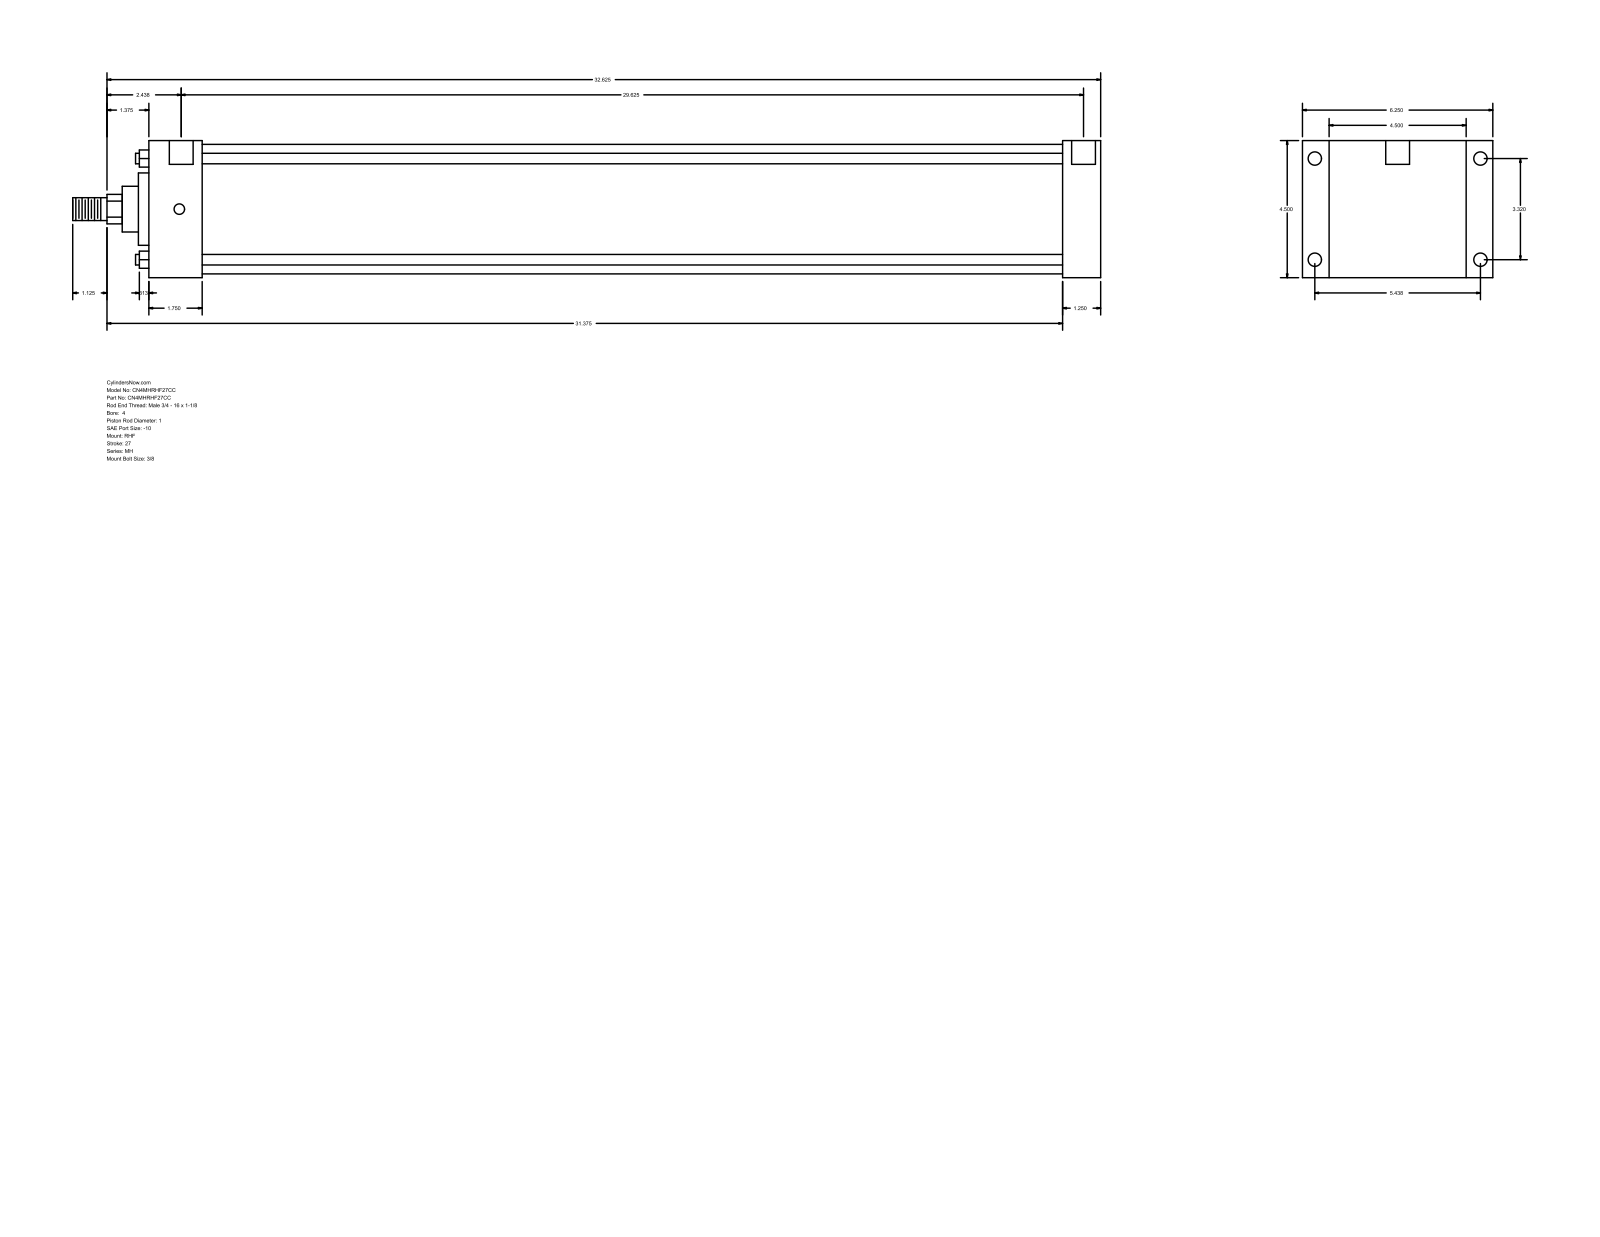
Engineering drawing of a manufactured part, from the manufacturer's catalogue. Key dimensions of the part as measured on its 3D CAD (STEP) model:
Part name (STEP PRODUCT): MH_RHF__0400_1
STEP written by: GSSL Pune (CONFIG_CONTROL_DESIGN)
Units: millimetres
Bodies: 0 solids, 90 faces (61 planar, 29 cylindrical, 0 other)
Overall size (bounding box): 857.25 × 158.75 × 114.3
Round holes (diameter × count): ⌀8.73 ×4, ⌀11.13 ×4, ⌀19.84 ×2
Round bosses / shafts (diameter × count): ⌀8.76 ×4, ⌀107.95 ×1, ⌀60.33 ×1, ⌀38.1 ×1, ⌀25.4 ×1, ⌀19.05 ×1
Partial cylindrical surfaces — rounded edges, fillets, slot ends (radius × count): R12.29 ×1
Main face-to-face distances: 114.3, 793.75, 762, 31.75, 22.23, 136.53, 44.46, 717.54, 749.29, 158.76
Hole centre spacings: 84.32, 138.12, 161.82, 755.65, 1.58, 1.59, 752.48, 754.06
